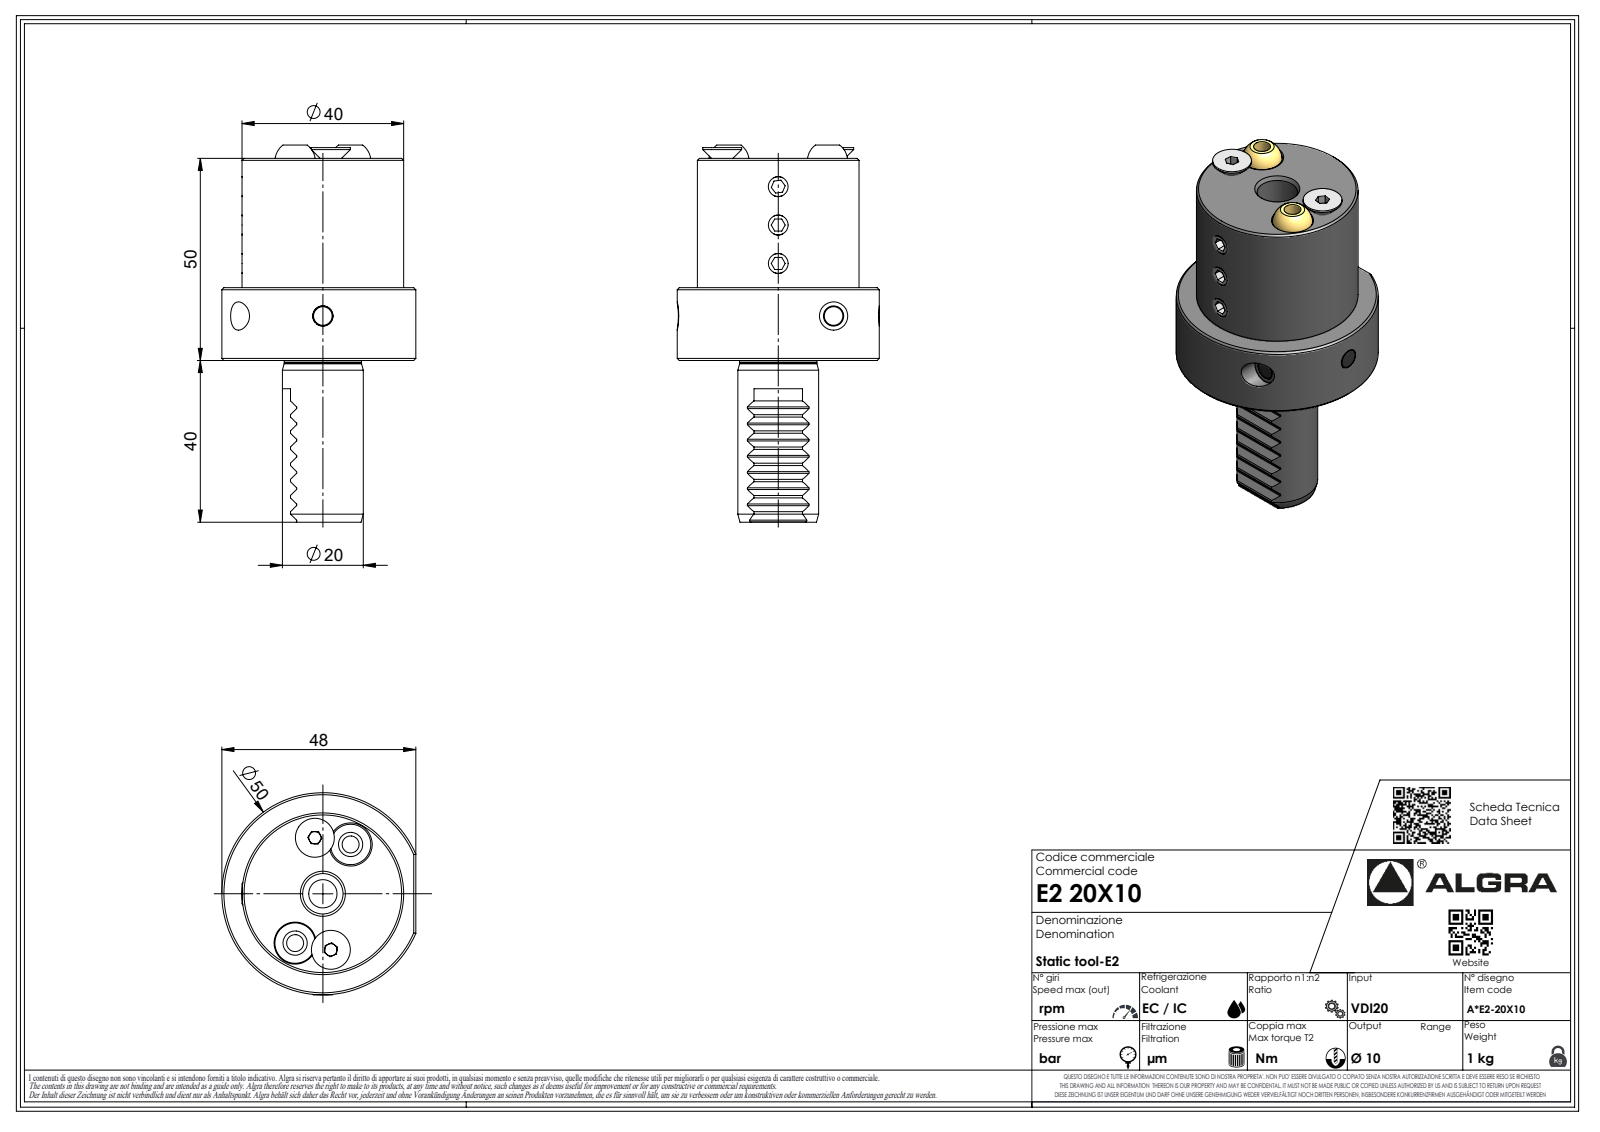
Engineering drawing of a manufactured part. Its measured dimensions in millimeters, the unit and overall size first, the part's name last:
Units: millimetres
Overall size (bounding box): 90 × 50 × 46
Round holes (diameter × count): ⌀1.57 ×1, ⌀10 ×1
Round bosses / shafts (diameter × count): ⌀50 ×1, ⌀40 ×1, ⌀20 ×1, ⌀19.1 ×1, ⌀4.77 ×1, ⌀1.28 ×1
Partial cylindrical surfaces — rounded edges, fillets, slot ends (radius × count): R0.3 ×8, R0.25 ×7, R0.39 ×7, R2.78 ×7, R0.16 ×1
Main face-to-face distances: 50, 18, 32, 2.83, 40, 58, 90, 5.66, 8.48, 14.14
Volume: 83 128 mm³ · Surface area: 14 228 mm²
Bodies: 1 solid, 252 faces (170 planar, 39 cylindrical, 43 other)
Part name (STEP PRODUCT): E220X10
STEP written by: SolidWorks 2023 (AUTOMOTIVE_DESIGN)
